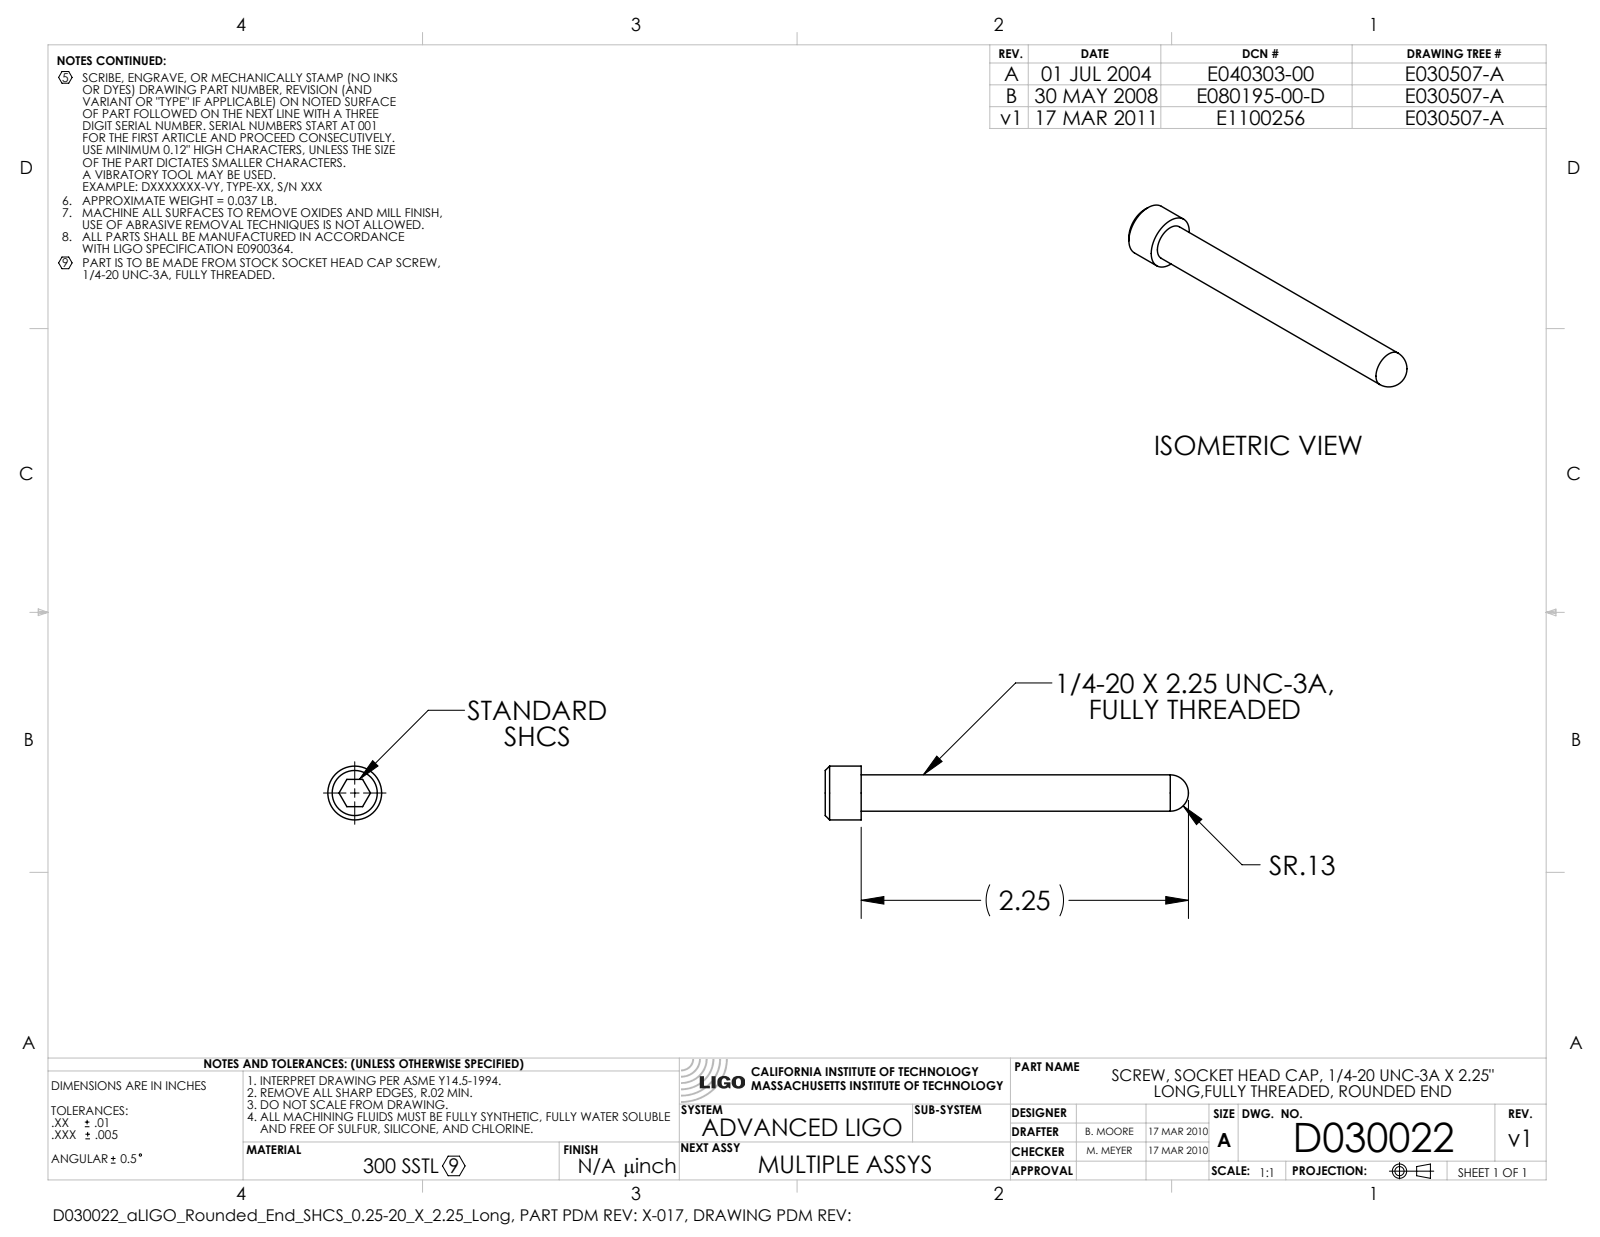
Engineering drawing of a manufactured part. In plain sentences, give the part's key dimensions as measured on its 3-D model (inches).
The part is named "D030022-v1_aLIGO_Rounded_End_SHCS_0.25-20_X_2.25_Long". Its 3-D file was written by "SolidWorks 2010 (AUTOMOTIVE_DESIGN)". It is 1 solid with 17 faces: 9 planar, 4 cylindrical and 4 other. Overall it measures 2.497 by 0.37 by 0.37 inches. Its volume is 0.131 cubic inches and its surface area 2.277 square inches. Round bosses or shafts: 1 of diameter 0.37, 1 of diameter 0.25. The main face-to-face distances are 0.247, 0.187, 0.127, 0.12.
